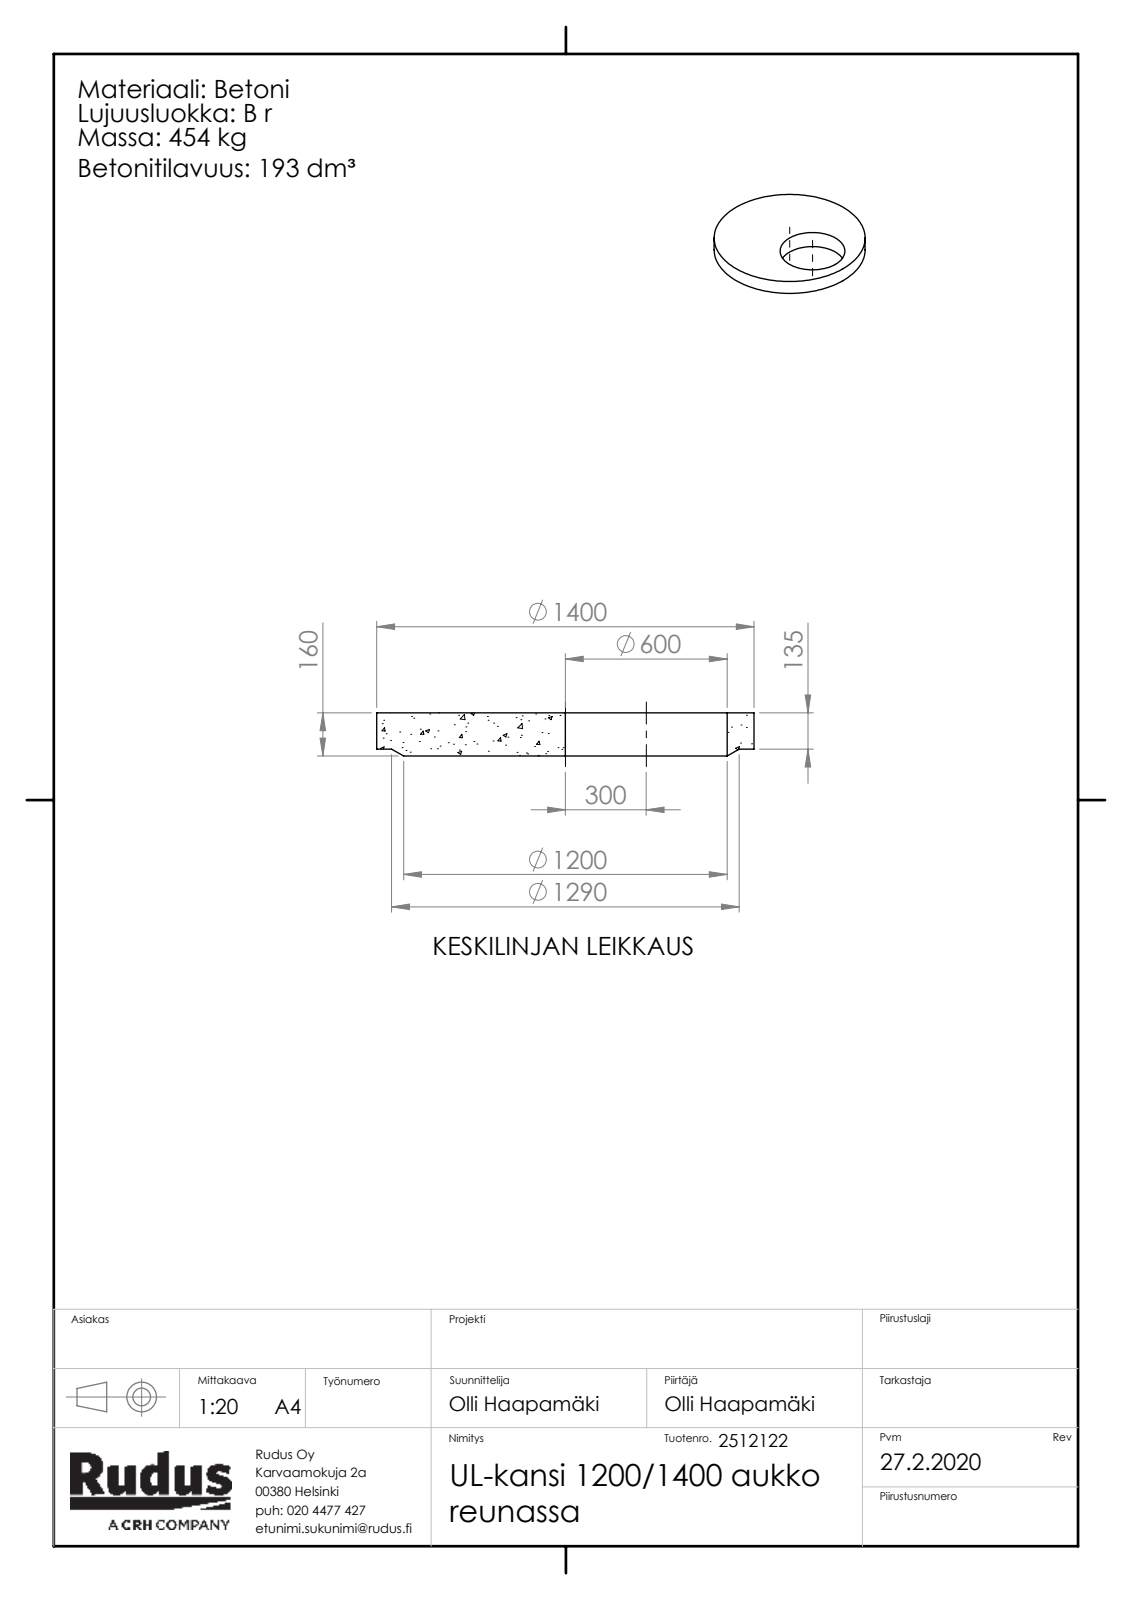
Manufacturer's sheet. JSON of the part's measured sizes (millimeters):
{"part_name": "UL-osa-kansi_aukko; Rudus 2512122 UL-kansi 1200_1400 aukko reunassa", "step_written_by": "SolidWorks 2019 (CONFIG_CONTROL_DESIGN)", "units": "millimeters", "bodies": {"solids": 1, "faces": 9, "planar": 3, "cylindrical": 4, "other": 2}, "overall_size": [1400, 1400, 160], "volume_mm3": 193000000, "surface_area_mm2": 3434000, "round_holes": [[600, 1]], "round_bosses_or_shafts": [[1400, 1]], "face_to_face_distances": [160, 25, 135]}
